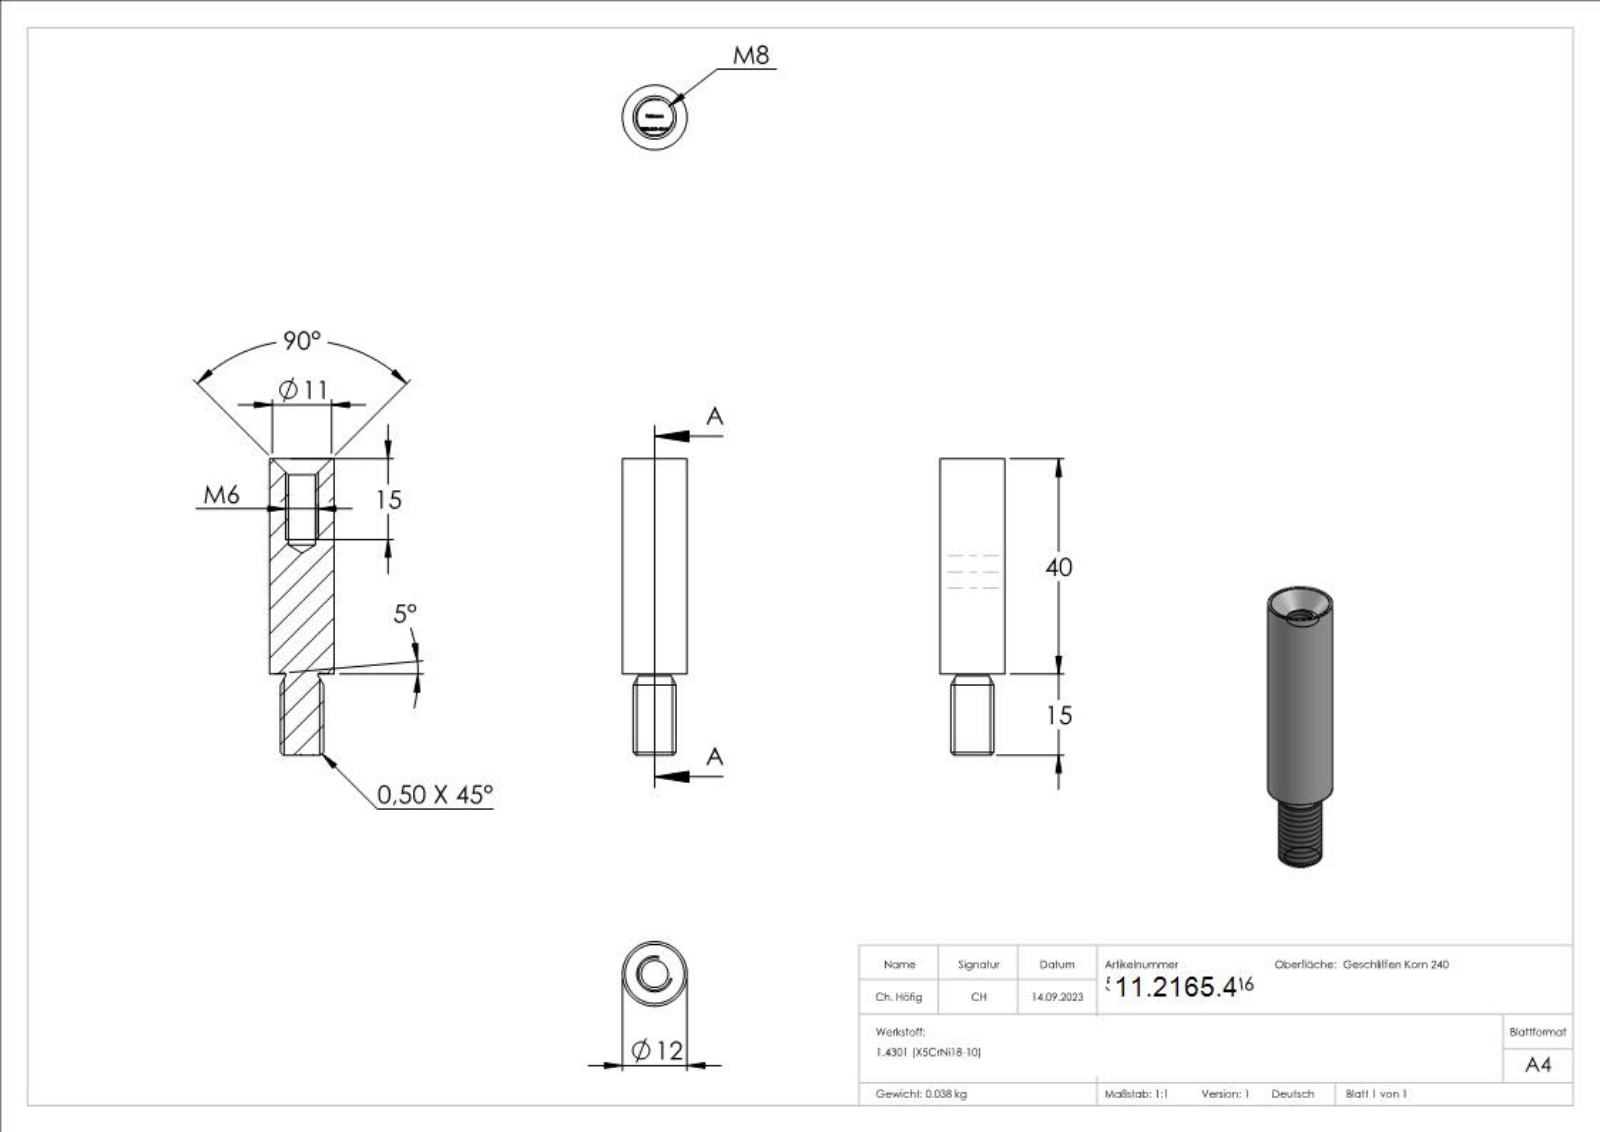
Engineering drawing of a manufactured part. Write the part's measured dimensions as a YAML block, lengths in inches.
part_name: "50236-240-40-M6"
step_written_by: "SolidWorks 2018 (CONFIG_CONTROL_DESIGN)"
units: inches
bodies: {solids: 1, faces: 269, planar: 157, cylindrical: 3, other: 109}
overall_size: [2.165, 0.472, 0.472]
volume: 0.294
surface_area: 3.674
round_holes:
  - {diameter: 0.197, count: 1}
round_bosses_or_shafts:
  - {diameter: 0.472, count: 1}
  - {diameter: 0.315, count: 1}
face_to_face_distances: [2.165, 2.161, 0.03, 0.051, 0.094, 0.094, 0.028, 0.061, 0.096, 0.022]
